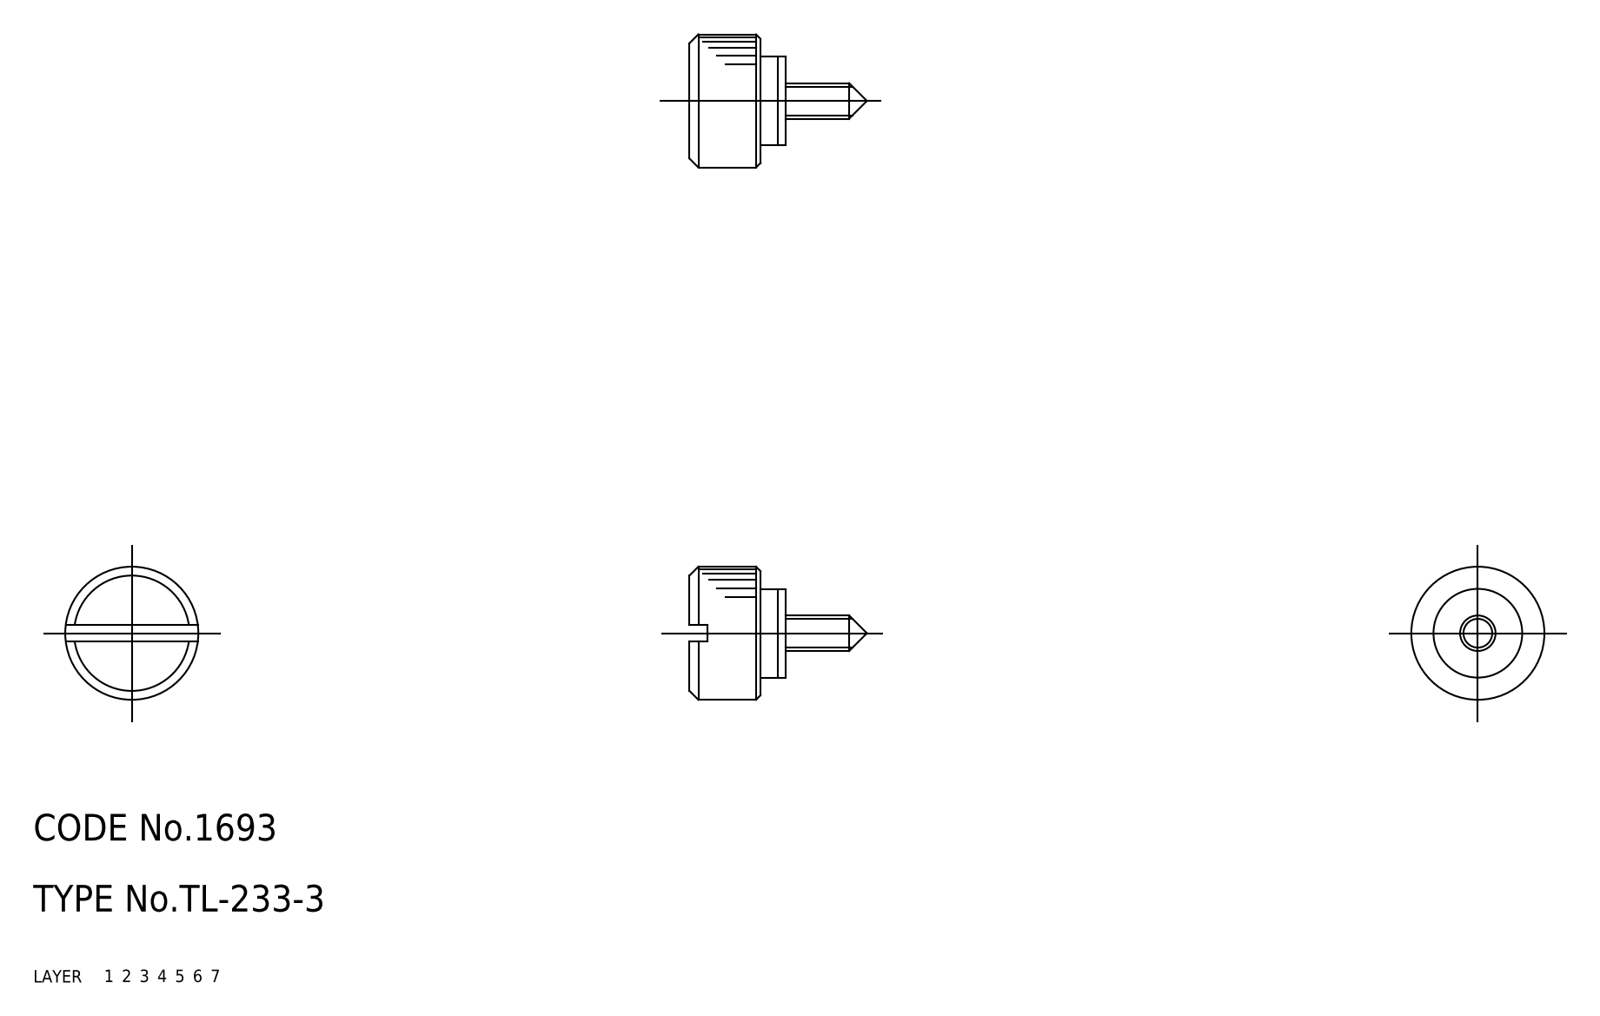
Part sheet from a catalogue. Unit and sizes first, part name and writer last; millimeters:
Units: millimetres
Overall size (bounding box): 20 × 15 × 15
Volume: 1 651 mm³ · Surface area: 1 067 mm²
Bodies: 2 solids, 37 faces (0 planar, 0 cylindrical, 37 other)
Part name (STEP PRODUCT): washer; knob; TL_233_3_29061_36
STEP written by: CADfix (AUTOMOTIVE_DESIGN)
